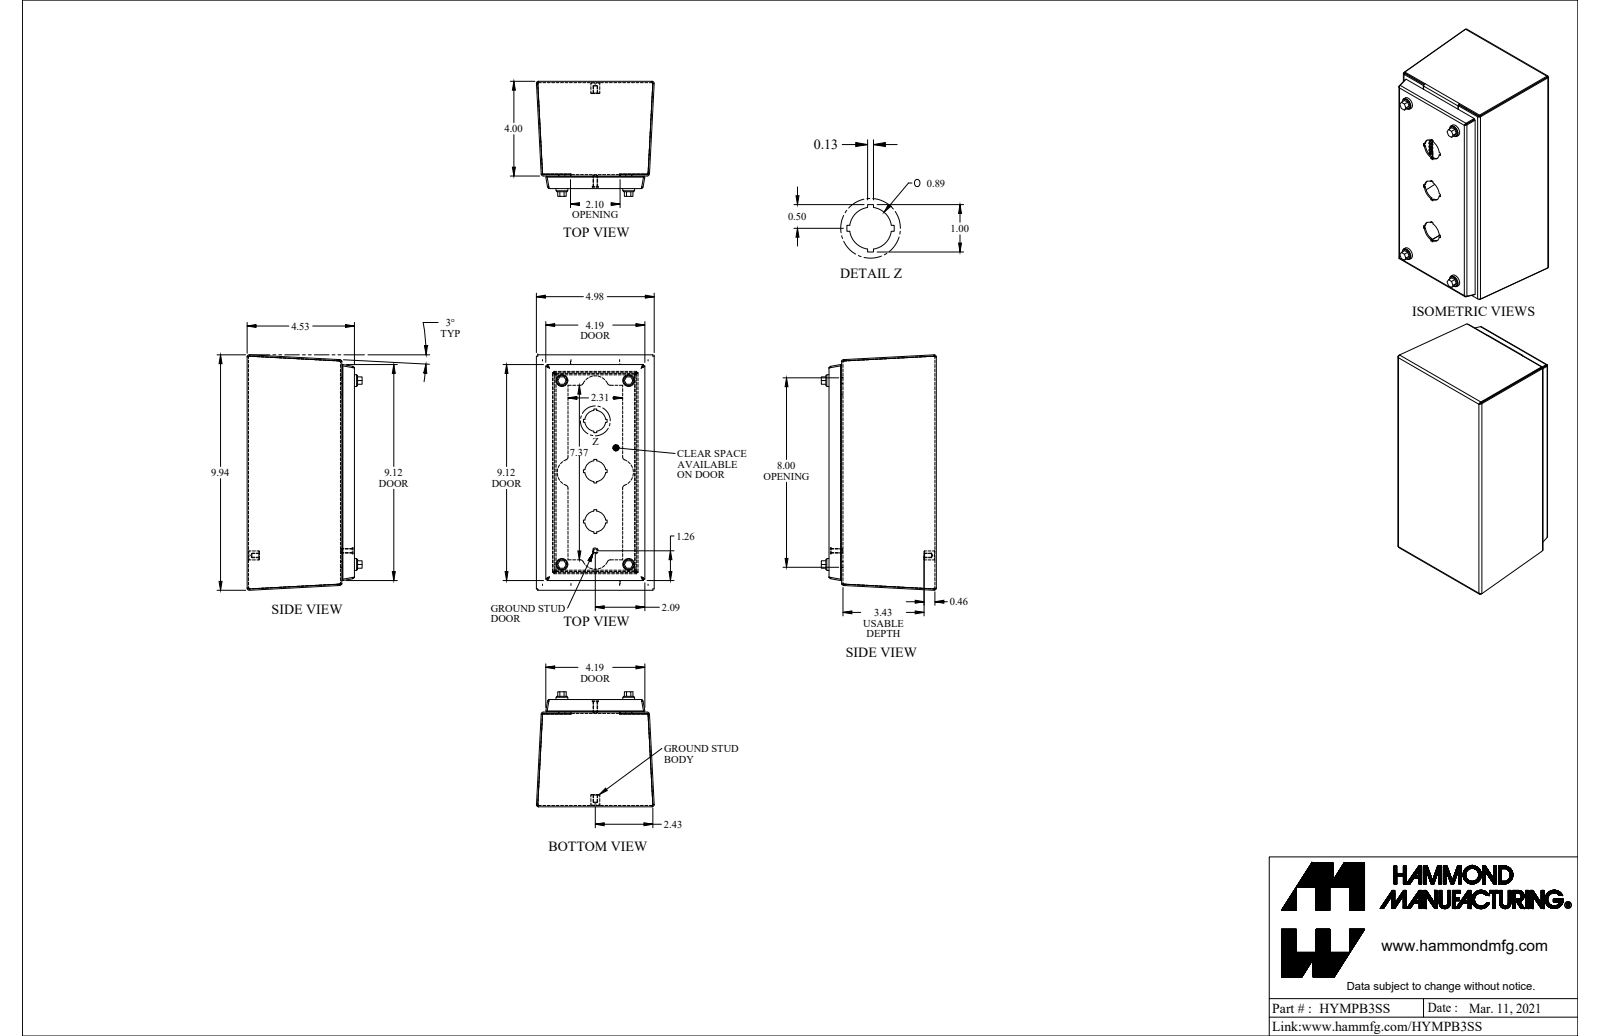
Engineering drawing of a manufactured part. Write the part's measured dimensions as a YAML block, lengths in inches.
part_name: "HYMPB3SS"
step_written_by: "SolidWorks 2021 (AUTOMOTIVE_DESIGN)"
units: inches
bodies: {solids: 22, faces: 491, planar: 328, cylindrical: 140, other: 23}
overall_size: [9.942, 4.976, 4.859]
volume: 17.6
surface_area: 564.2
round_holes:
  - {diameter: 0.065, count: 4}
  - {diameter: 0.235, count: 4}
  - {diameter: 0.239, count: 4}
  - {diameter: 0.24, count: 4}
  - {diameter: 0.25, count: 4}
  - {diameter: 0.253, count: 4}
  - {diameter: 0.4, count: 4}
  - {diameter: 0.886, count: 3}
  - {diameter: 0.156, count: 1}
round_bosses_or_shafts:
  - {diameter: 0.375, count: 5}
  - {diameter: 0.19, count: 5}
  - {diameter: 0.5, count: 4}
  - {diameter: 0.45, count: 4}
  - {diameter: 0.406, count: 4}
  - {diameter: 0.315, count: 4}
  - {diameter: 0.25, count: 1}
partial_cylinders:
  - {radius: 0.029, count: 16}
  - {radius: 0.086, count: 16}
  - {radius: 0.125, count: 8}
  - {radius: 0.055, count: 4}
  - {radius: 0.076, count: 4}
  - {radius: 0.5, count: 4}
  - {radius: 0.575, count: 4}
face_to_face_distances: [0.057, 4.418, 4.475, 3.943, 0.057, 4.532, 4.475, 0.475, 4, 0.532]
hole_center_spacings: [7.766, 8.262, 2.819, 7.766, 8.261, 2.819, 2.298, 6.115]
